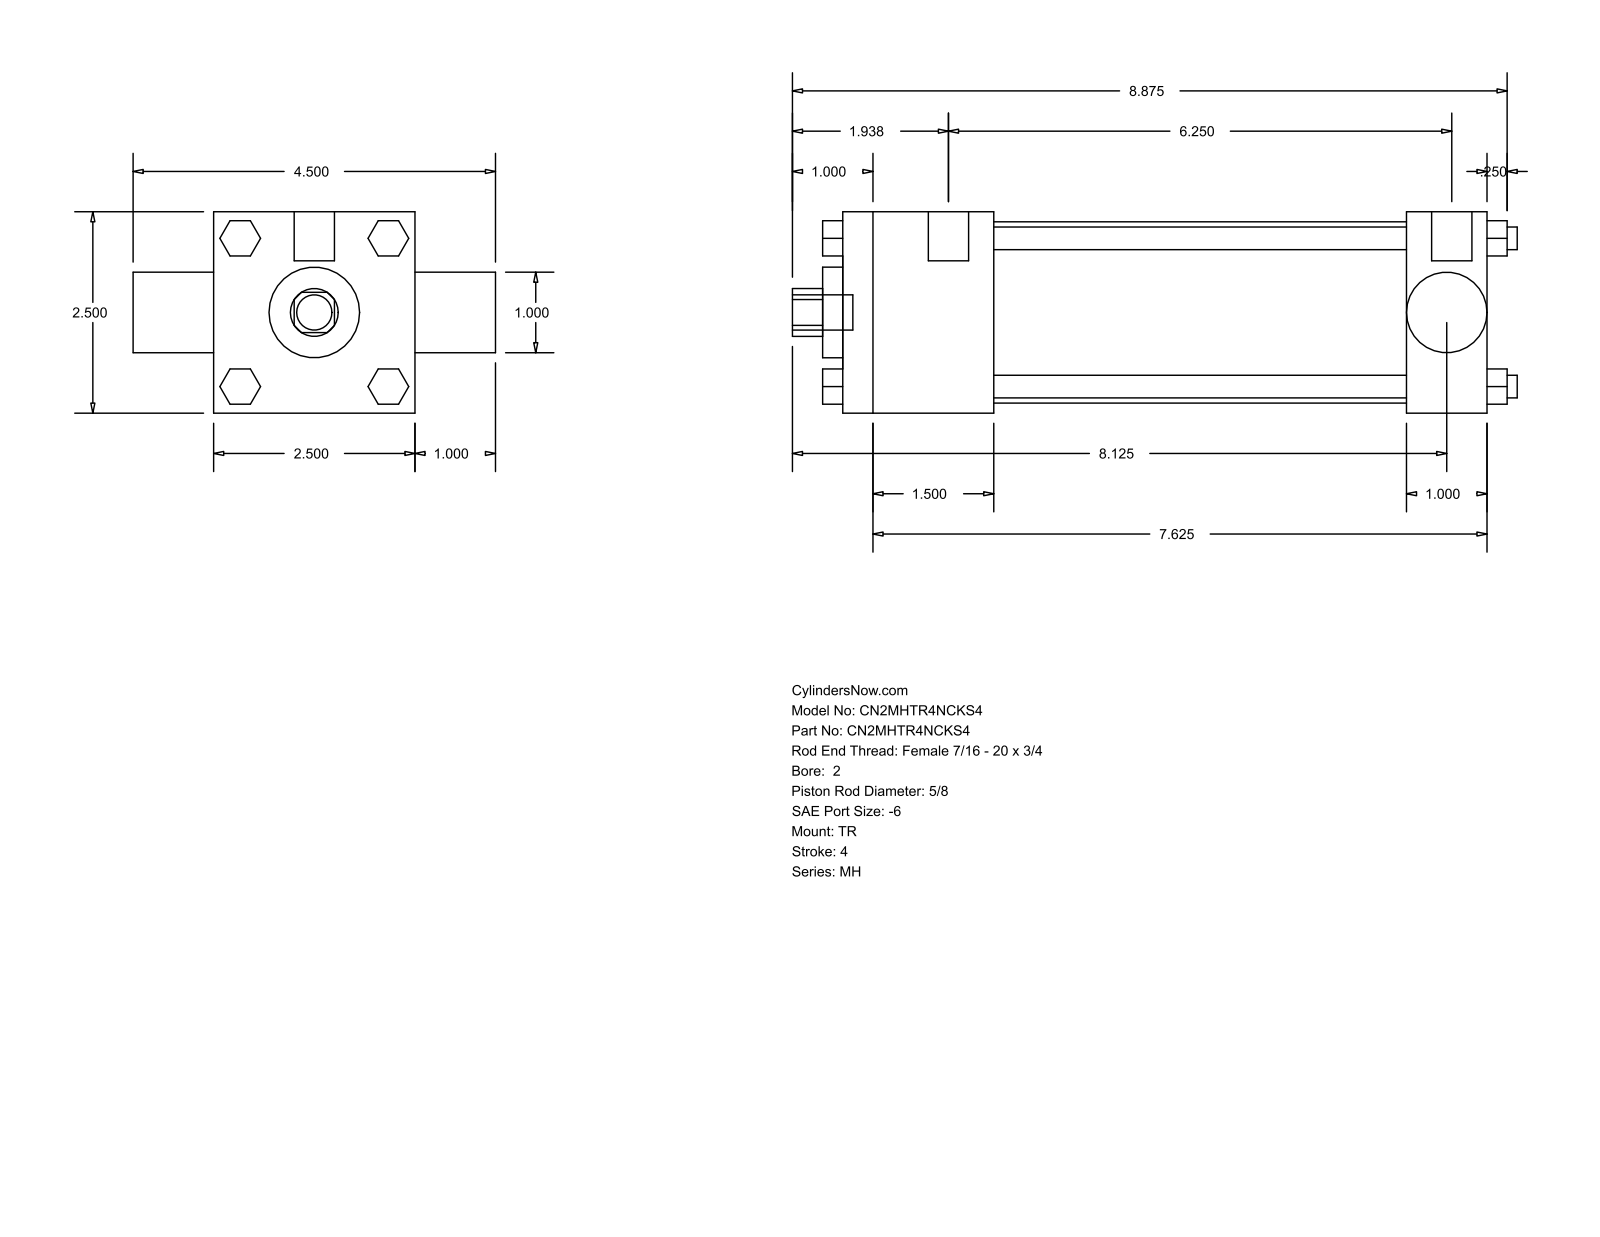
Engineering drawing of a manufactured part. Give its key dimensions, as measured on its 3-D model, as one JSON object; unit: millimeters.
{"part_name": "MH_TR__0200_0.625", "step_written_by": "GSSL Pune (CONFIG_CONTROL_DESIGN)", "units": "millimeters", "bodies": {"solids": 0, "faces": 120, "planar": 92, "cylindrical": 28, "other": 0}, "overall_size": [228.6, 114.3, 63.5], "round_holes": [[15.88, 1], [25.35, 1], [28.57, 1], [57.15, 1]], "round_bosses_or_shafts": [[7.14, 4], [5.56, 3], [12.7, 2], [11.11, 1]], "partial_cylinders_radius": [[7.54, 1]], "face_to_face_distances": [63.5, 203.19, 47.62, 177.8, 130.18, 155.57, 25.39, 25.4, 88.9, 6.35]}
